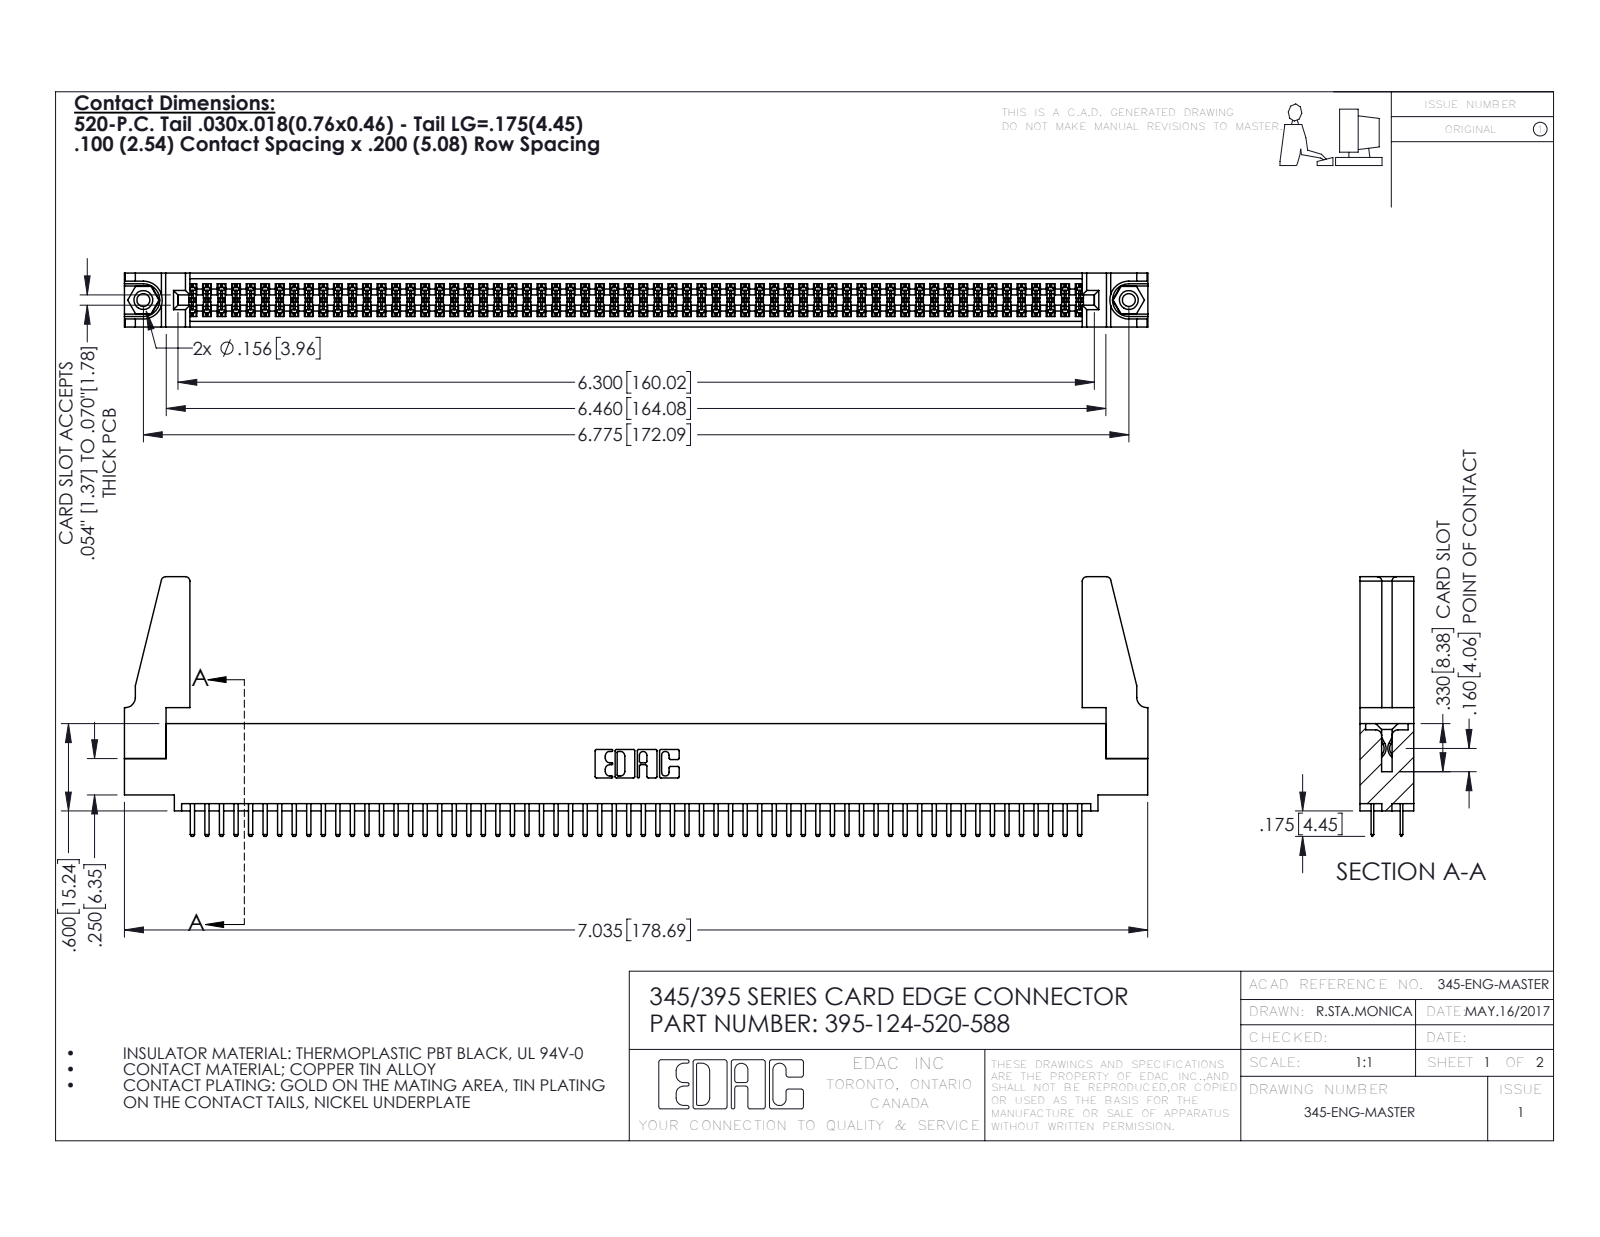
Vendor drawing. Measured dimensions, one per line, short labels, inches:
name: 345-250-001_345-250-001-102; 395-124-520-588; 345-292-001_345-293-120; 345-220-078_345-220-088 (+1 more)
written by: SolidWorks 2016 (CONFIG_CONTROL_DESIGN)
unit: in
bodies: 129 solids, 6950 faces (4496 planar, 2438 cylindrical, 16 other)
size: 7.036 × 1.785 × 0.37
volume: 1.261 in³; area: 45.31 in²
holes: 2× ⌀0.089, 2× ⌀0.125, 2× ⌀0.156, 1× ⌀0.064
bosses: 2× ⌀0.155
rounds: 186× R0.006, 128× R0.01, 22× R0.01, 8× R0.03, 6× R0.007, 6× R0.031, 3× R0.026, 2× R0.014
face distances: 0.072, 0.298, 0.37, 0.2, 0.098, 0.272, 0.025, 0.225, 0.022, 0.072
hole spacings: 0.27, 6.539, 6.775
